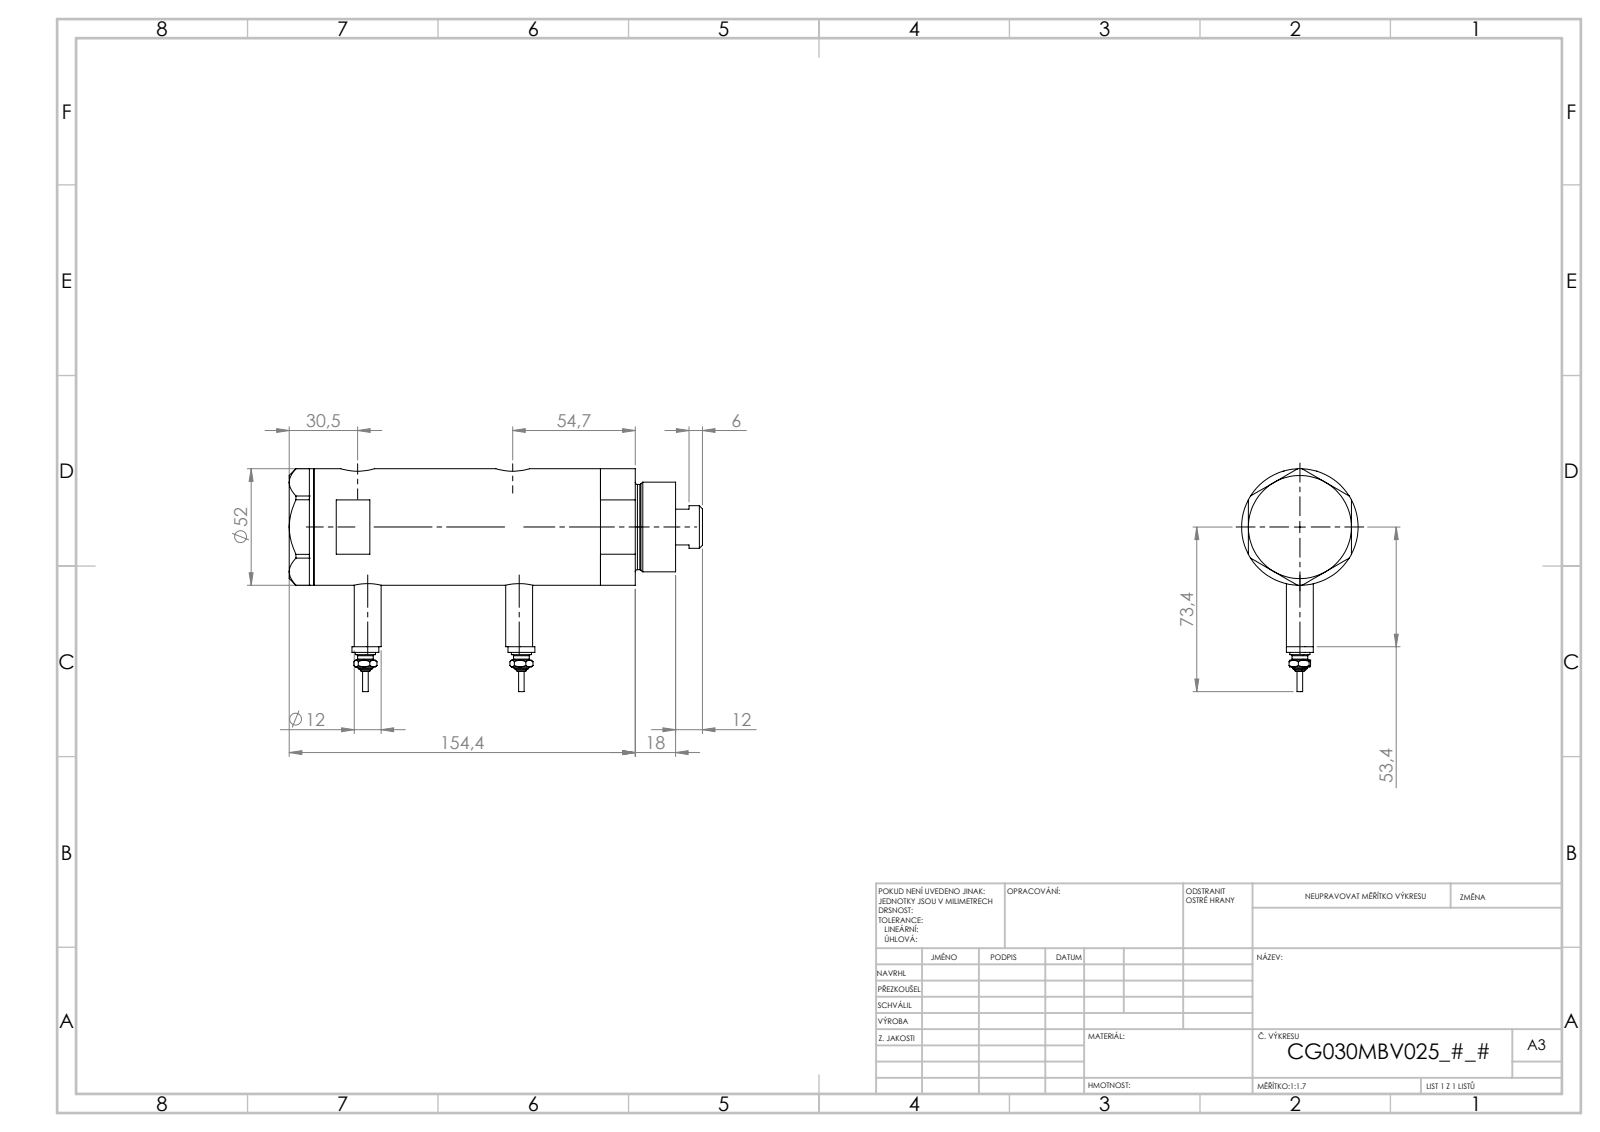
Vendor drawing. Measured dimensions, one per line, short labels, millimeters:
name: V270CG_BACK; V270CG_MIDDLE; Switch; V270CG_VC (+1 more)
written by: SolidWorks 2019 (CONFIG_CONTROL_DESIGN)
unit: mm
bodies: 6 solids, 226 faces (93 planar, 69 cylindrical, 64 other)
size: 184.4 × 99.4 × 52
volume: 342 898 mm³; area: 80 070 mm²
holes: 2× ⌀9.73, 2× ⌀12.5, 2× ⌀15, 1× ⌀6.5, 1× ⌀20, 1× ⌀21.5, 1× ⌀30, 1× ⌀33, 1× ⌀44
bosses: 4× ⌀12, 2× ⌀9, 2× ⌀7, 2× ⌀4.5, 2× ⌀2.5, 1× ⌀52, 1× ⌀40, 1× ⌀38
face distances: 91.5, 23.8, 67.7, 11, 34.8, 102.5, 46, 36.4, 138.9, 127.9
hole spacings: 2.9, 4.5, 64.7, 67.6, 69.2, 72.1
